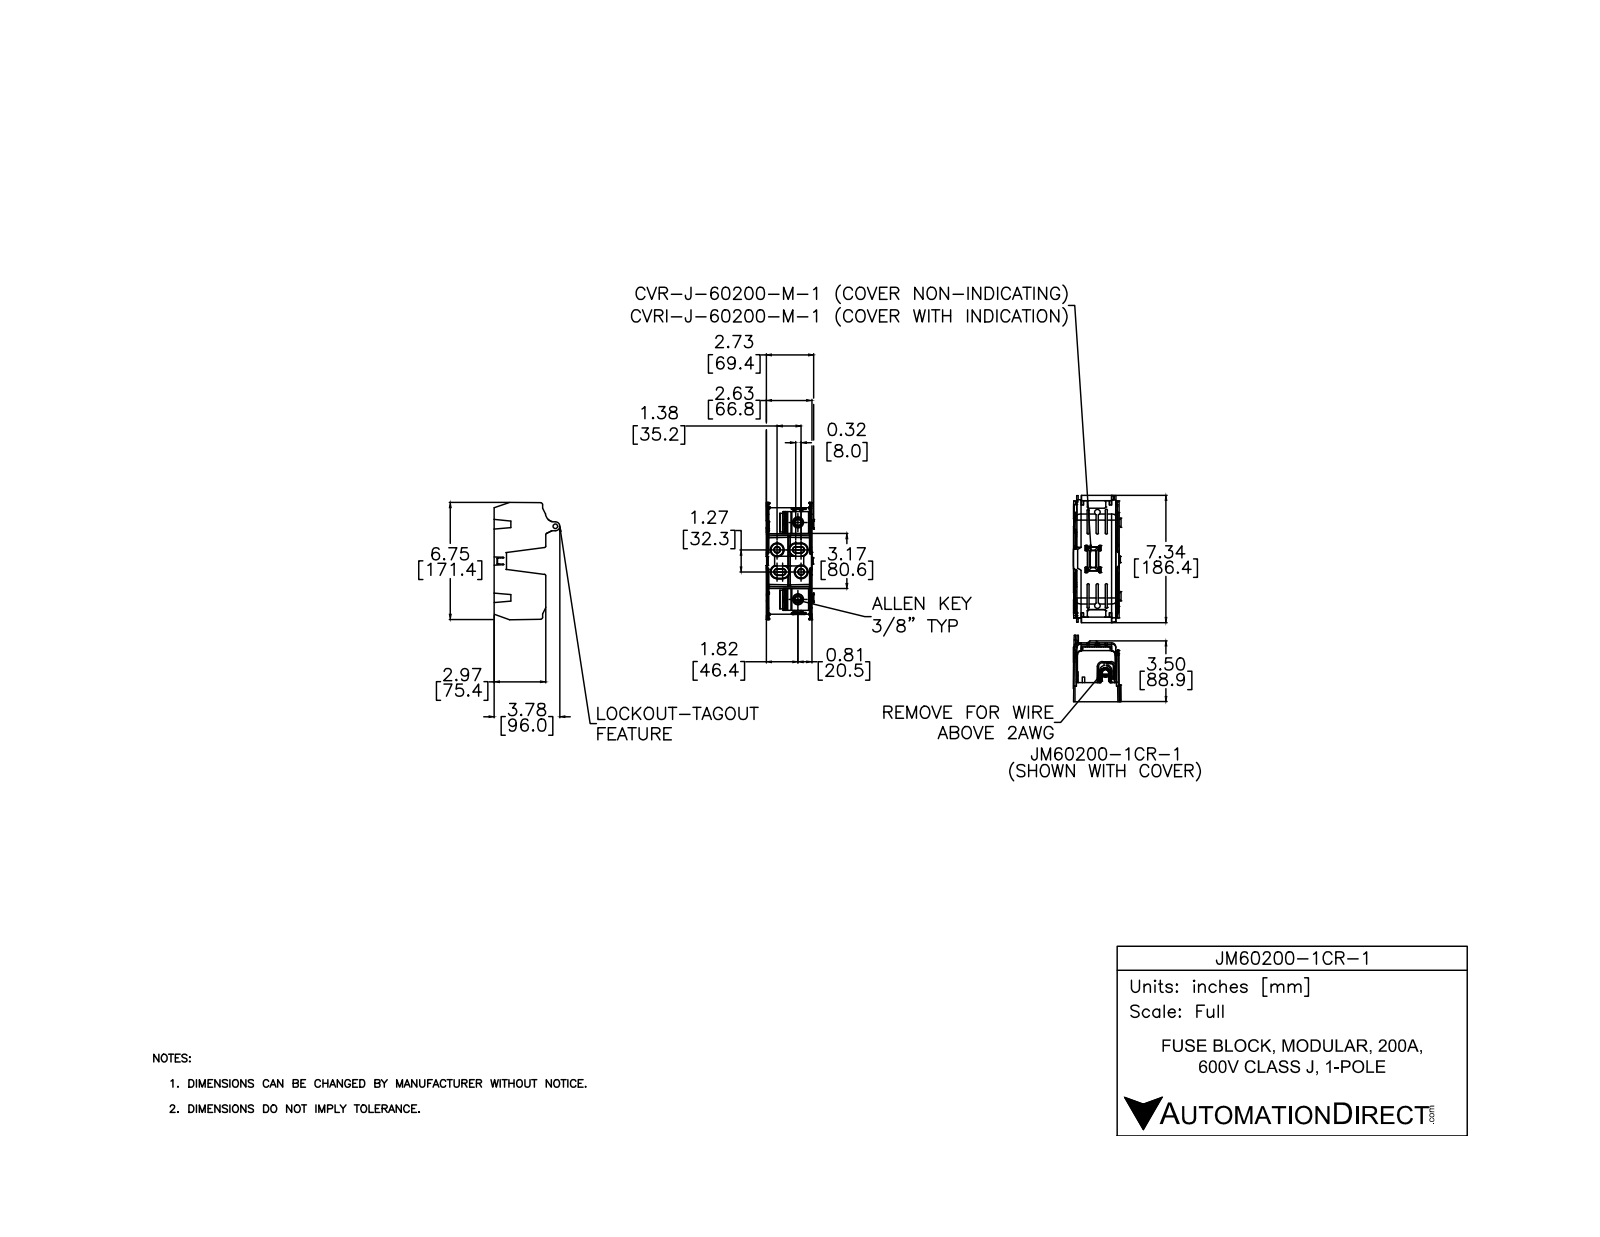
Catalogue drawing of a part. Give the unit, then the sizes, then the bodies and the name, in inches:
Units: inches
Overall size (bounding box): 6.757 × 3.779 × 2.731
Round bosses / shafts (diameter × count): ⌀0.197 ×4, ⌀0.625 ×3, ⌀0.406 ×2, ⌀0.277 ×1, ⌀0.04 ×1
Partial cylindrical surfaces — rounded edges, fillets, slot ends (radius × count): R0.02 ×102, R0.01 ×42, R0.01 ×28, R0.079 ×13, R0.01 ×10, R0.015 ×6, R0.119 ×6, R0.039 ×5
Main face-to-face distances: 2.502, 2.503, 1.108, 0.048, 0.032, 4.427, 1.26, 1.156, 1.188, 0.08
Bodies: 0 solids, 817 faces (241 planar, 344 cylindrical, 232 other)
Part name (STEP PRODUCT): JM60200-1CR-1
STEP written by: SolidWorks 2021 (CONFIG_CONTROL_DESIGN)
